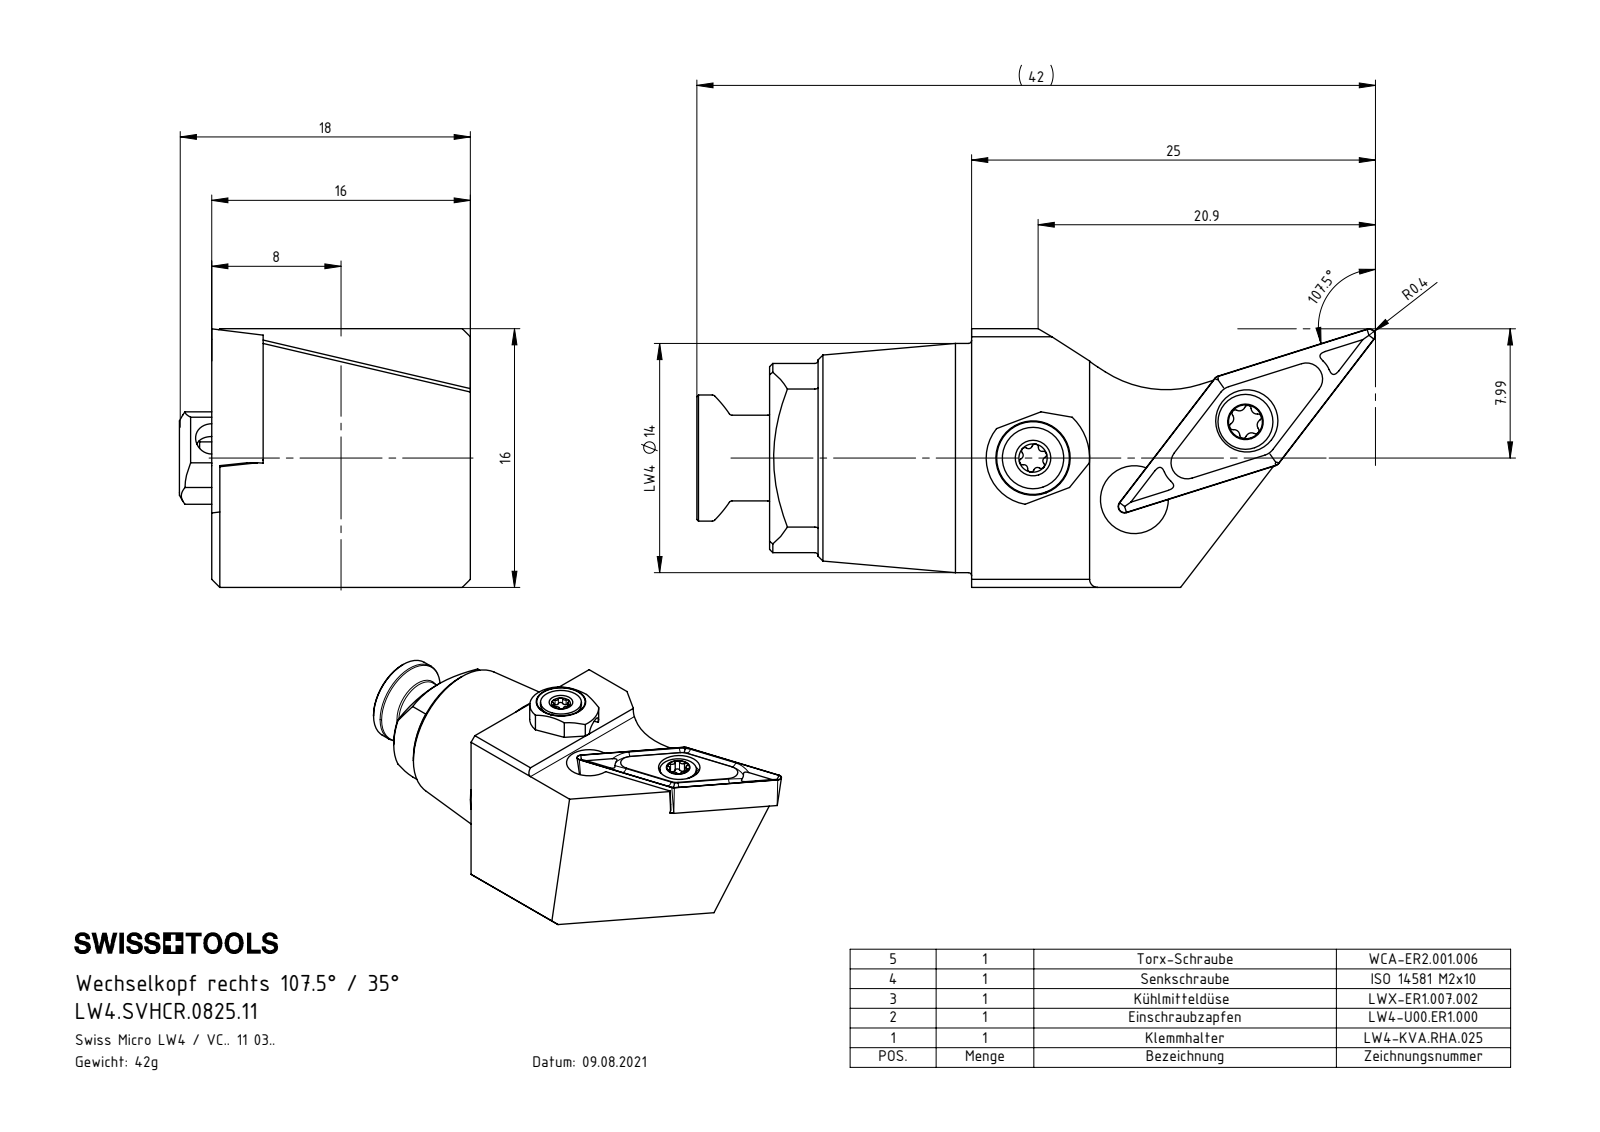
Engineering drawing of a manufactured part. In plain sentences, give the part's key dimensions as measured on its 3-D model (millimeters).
The part is named "LW4-KVA.RHA.025_A; LW4.SVHCR.0825.11; VCGT110304; WCA-ER2.001.006_A (+1 more)". Its 3-D file was written by "SolidWorks 2022 (CONFIG_CONTROL_DESIGN)". It is 4 solids with 204 faces: 56 planar, 68 cylindrical and 80 other. Overall it measures 37.49 by 17.95 by 16 millimeters. Its volume is 4 832 cubic millimeters and its surface area 2 797 square millimeters. Round holes: 2 of diameter 2, 1 of diameter 1.6, 1 of diameter 2.05, 1 of diameter 2.8, 1 of diameter 3, 1 of diameter 3.85, 1 of diameter 4.2, 1 of diameter 5.5. Round bosses or shafts: 1 of diameter 14.17, 1 of diameter 3.8, 1 of diameter 3.4, 1 of diameter 2.5, 1 of diameter 2. Partial cylindrical surfaces (rounded edges, fillets, slot ends): 8 of radius 0.2, 6 of radius 0.21, 6 of radius 0.24, 4 of radius 0.36, 2 of radius 0.36, 1 of radius 0.5, 1 of radius 5.85, 1 of radius 7. The main face-to-face distances are 16, 12.82, 3.18, 15.5, 2.68, 0.5, 12.5, 4, 12, 3. The hole center spacings are 5.86, 8.39, 8.49, 10.54, 10.63.
